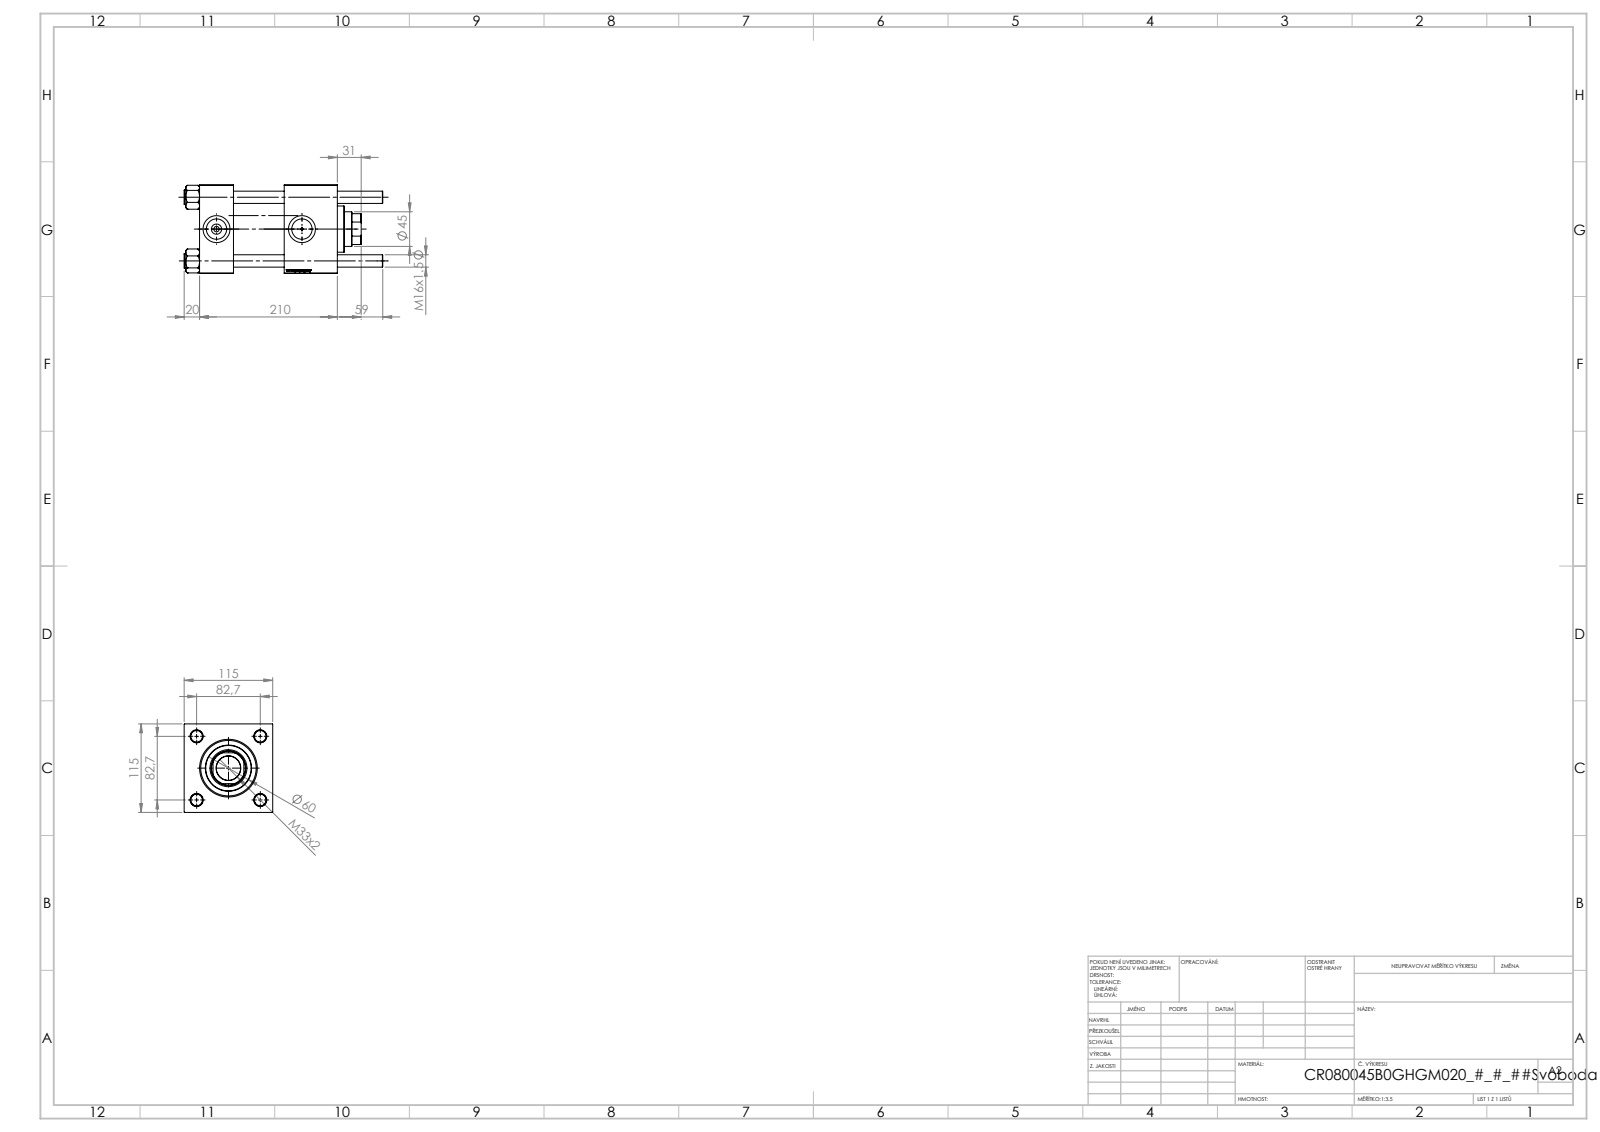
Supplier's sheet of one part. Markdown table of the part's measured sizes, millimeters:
| quantity | value |
| --- | --- |
| part name | V215CR_VCP_B; V215CR_B-1; V215CR_B_TYCINKA; V215_VC_A (+1 more) |
| STEP written by | SolidWorks 2019 (CONFIG_CONTROL_DESIGN) |
| units | millimeters |
| bodies | 11 solids, 1206 faces (480 planar, 78 cylindrical, 648 other) |
| overall size | 258 × 115 × 115 |
| volume | 1 899 000 mm³ |
| surface area | 299 785 mm² |
| round holes (diameter × count) | 16 × 4, 7 × 2, 26.44 × 2, 35 × 2, 31.5 × 1, 45 × 1, 48 × 1, 61 × 1, 72 × 1, 80 × 1 |
| round bosses / shafts (diameter × count) | 19 × 4, 86 × 1, 60 × 1 |
| partial cylindrical surfaces (radius × count) | 22 × 1 |
| main face-to-face distances | 115, 44, 110, 179, 135, 66, 69, 20, 150.3, 106.3 |
| hole center spacings | 58.48, 82.7, 116.96, 111 |
